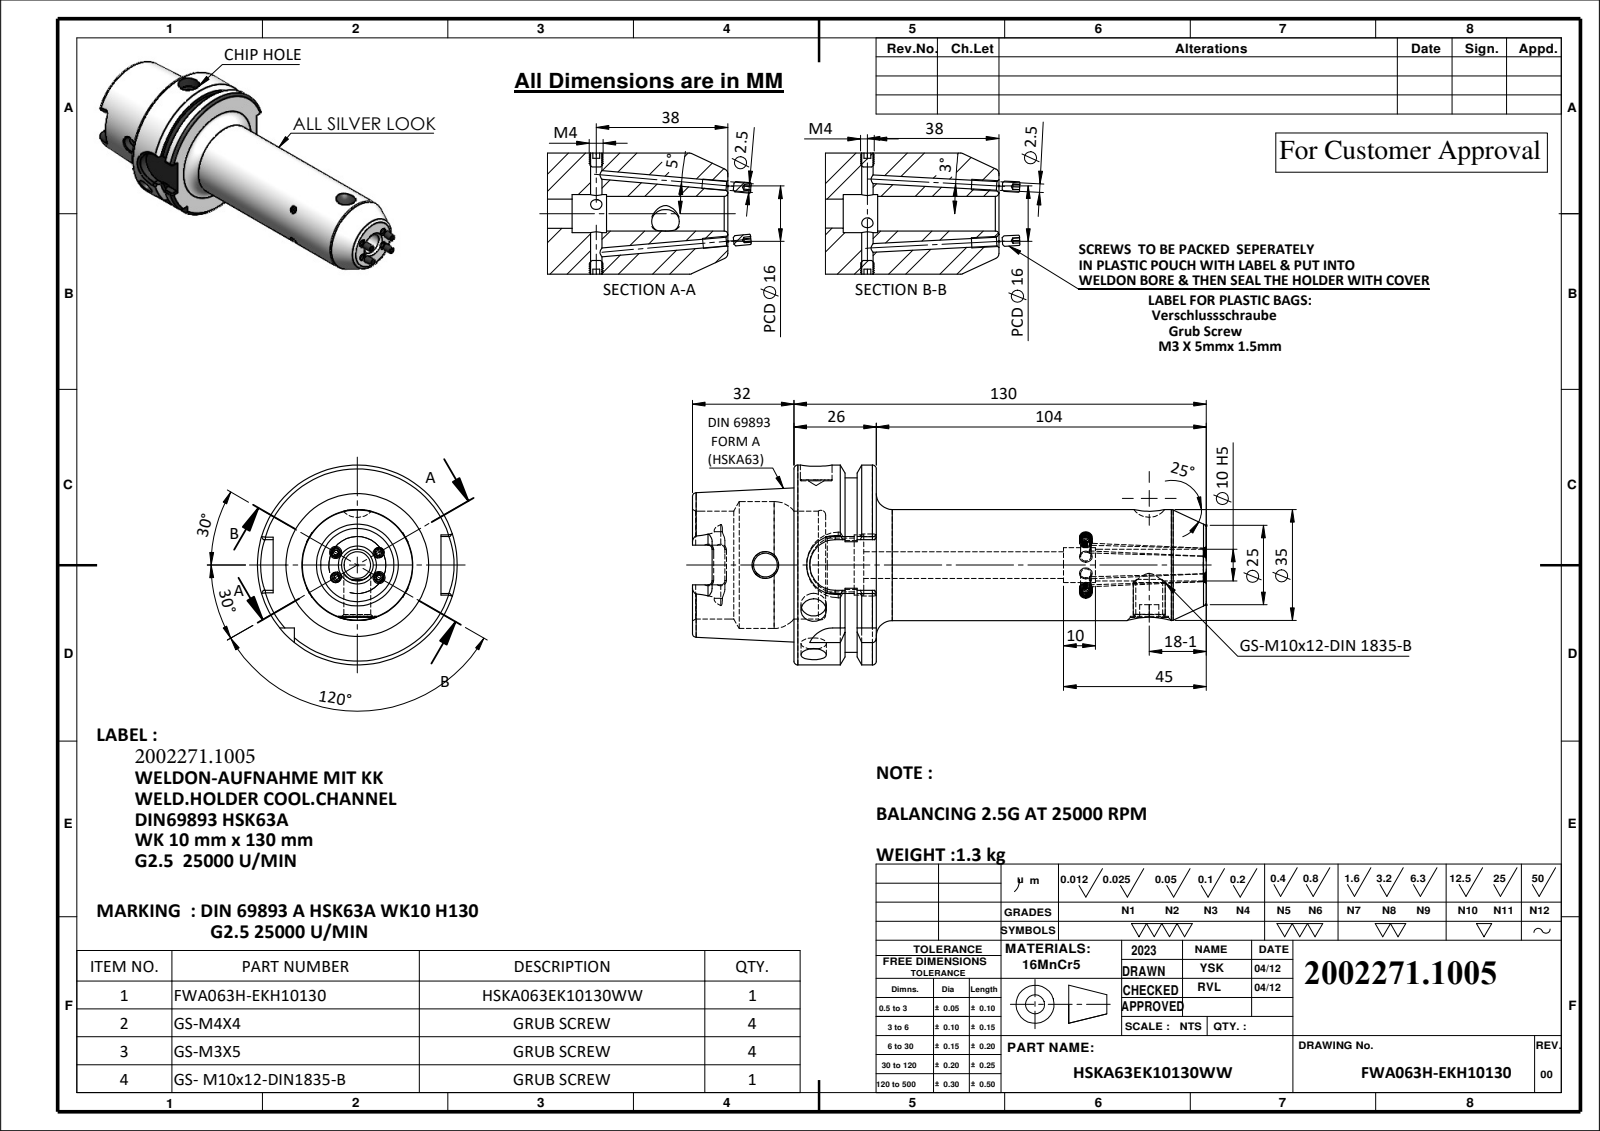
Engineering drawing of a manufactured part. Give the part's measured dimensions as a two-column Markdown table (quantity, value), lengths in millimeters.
| quantity | value |
| --- | --- |
| part name | HSKA63EK10130WW; GS-M4X4_DIN 913 - M4 x 4-N; FWA063H-EKH10130; GS-M3X5 (+1 more) |
| STEP written by | SolidWorks 2023 (CONFIG_CONTROL_DESIGN) |
| units | millimeters |
| bodies | 10 solids, 494 faces (153 planar, 121 cylindrical, 220 other) |
| overall size | 168.78 × 63 × 63 |
| volume | 170 915 mm³ |
| surface area | 39 026 mm² |
| round holes (diameter × count) | 2.5 × 4, 3.3 × 2, 8 × 2, 10 × 2, 7.5 × 1, 8.4 × 1, 8.5 × 1, 11 × 1, 12 × 1, 17 × 1, 19 × 1, 34 × 1 |
| round bosses / shafts (diameter × count) | 3 × 4, 4 × 2, 63 × 1, 55 × 1, 35 × 1, 10 × 1 |
| partial cylindrical surfaces (radius × count) | 1.3 × 6, 2.88 × 4, 8 × 2, 9 × 1 |
| main face-to-face distances | 25.95, 10, 15.95, 32, 42, 57.95, 52.9, 162, 130, 120 |
| hole center spacings | 105 |
